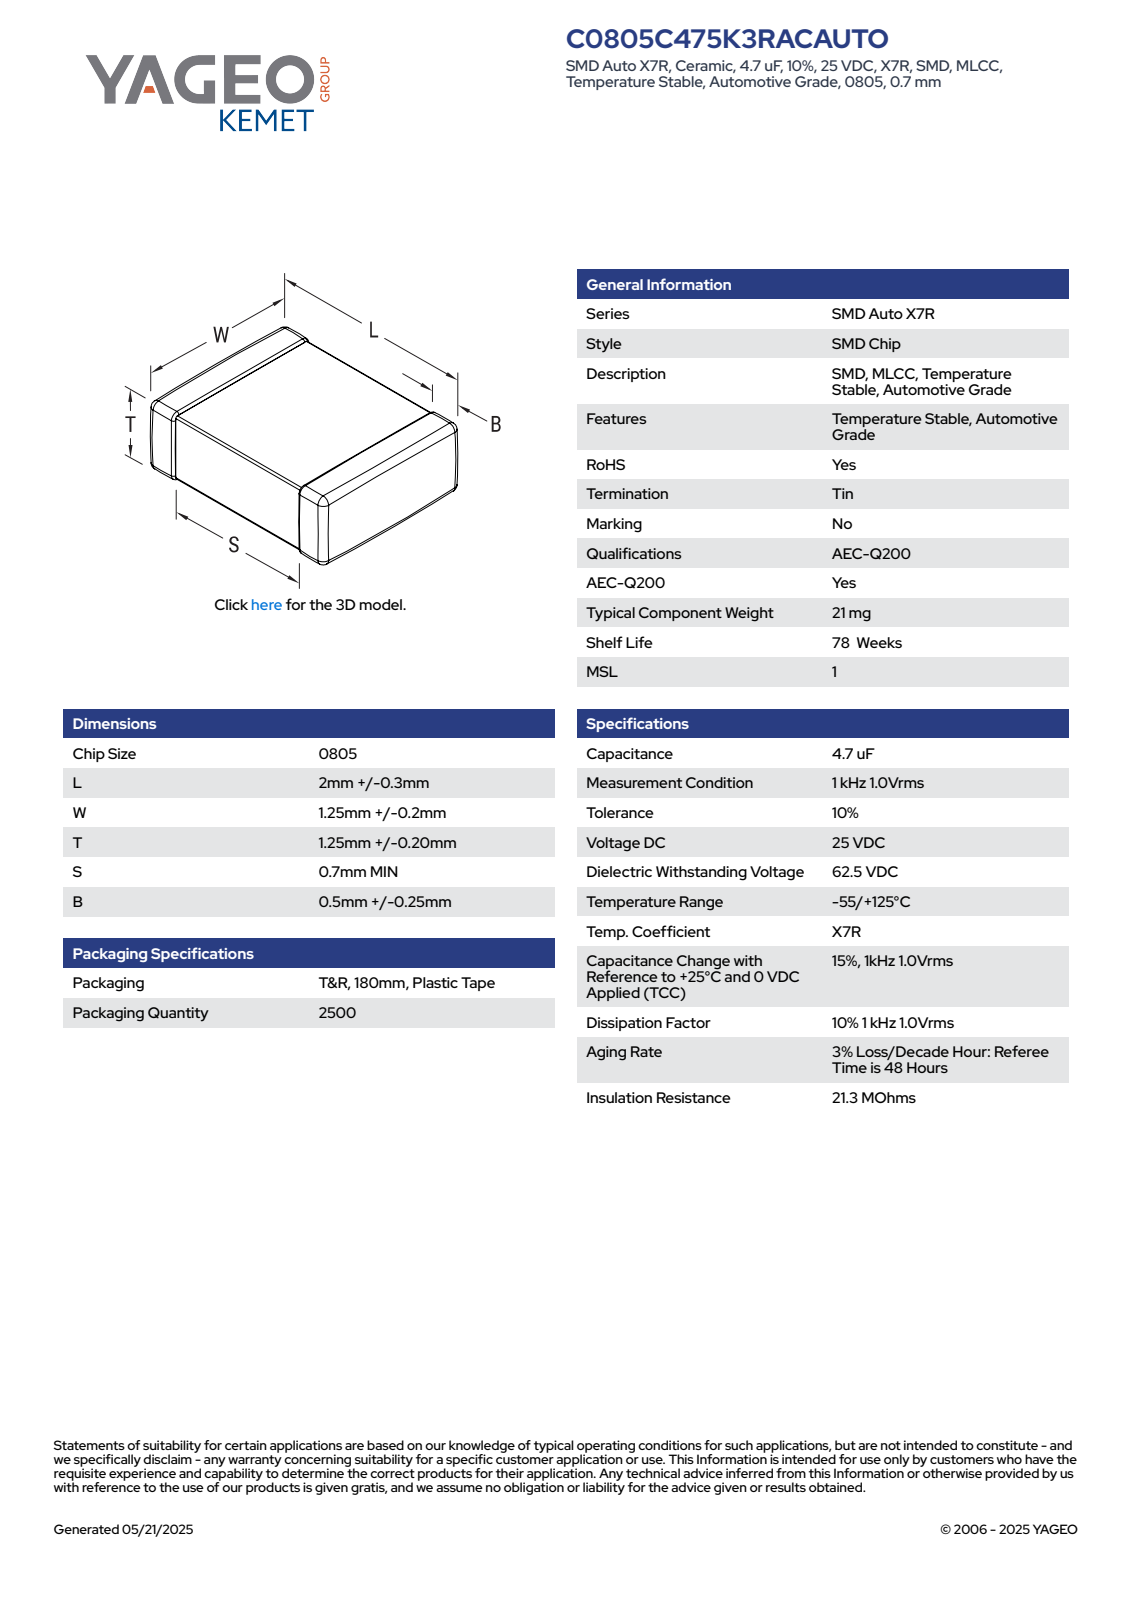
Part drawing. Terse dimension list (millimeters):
name: CCS_CCSTD_0805_L2.3W1.45T1.45B0.5
written by: SolidWorks 2014 (AUTOMOTIVE_DESIGN)
unit: mm
bodies: 4 solids, 121 faces (71 planar, 34 cylindrical, 16 other)
size: 2.3 × 1.45 × 1.45
volume: 5 mm³; area: 17 mm²
face distances: 1.42, 1.39, 1.45, 2.3, 1.03, 1.27, 1.24, 1.06, 1.15, 0.87
